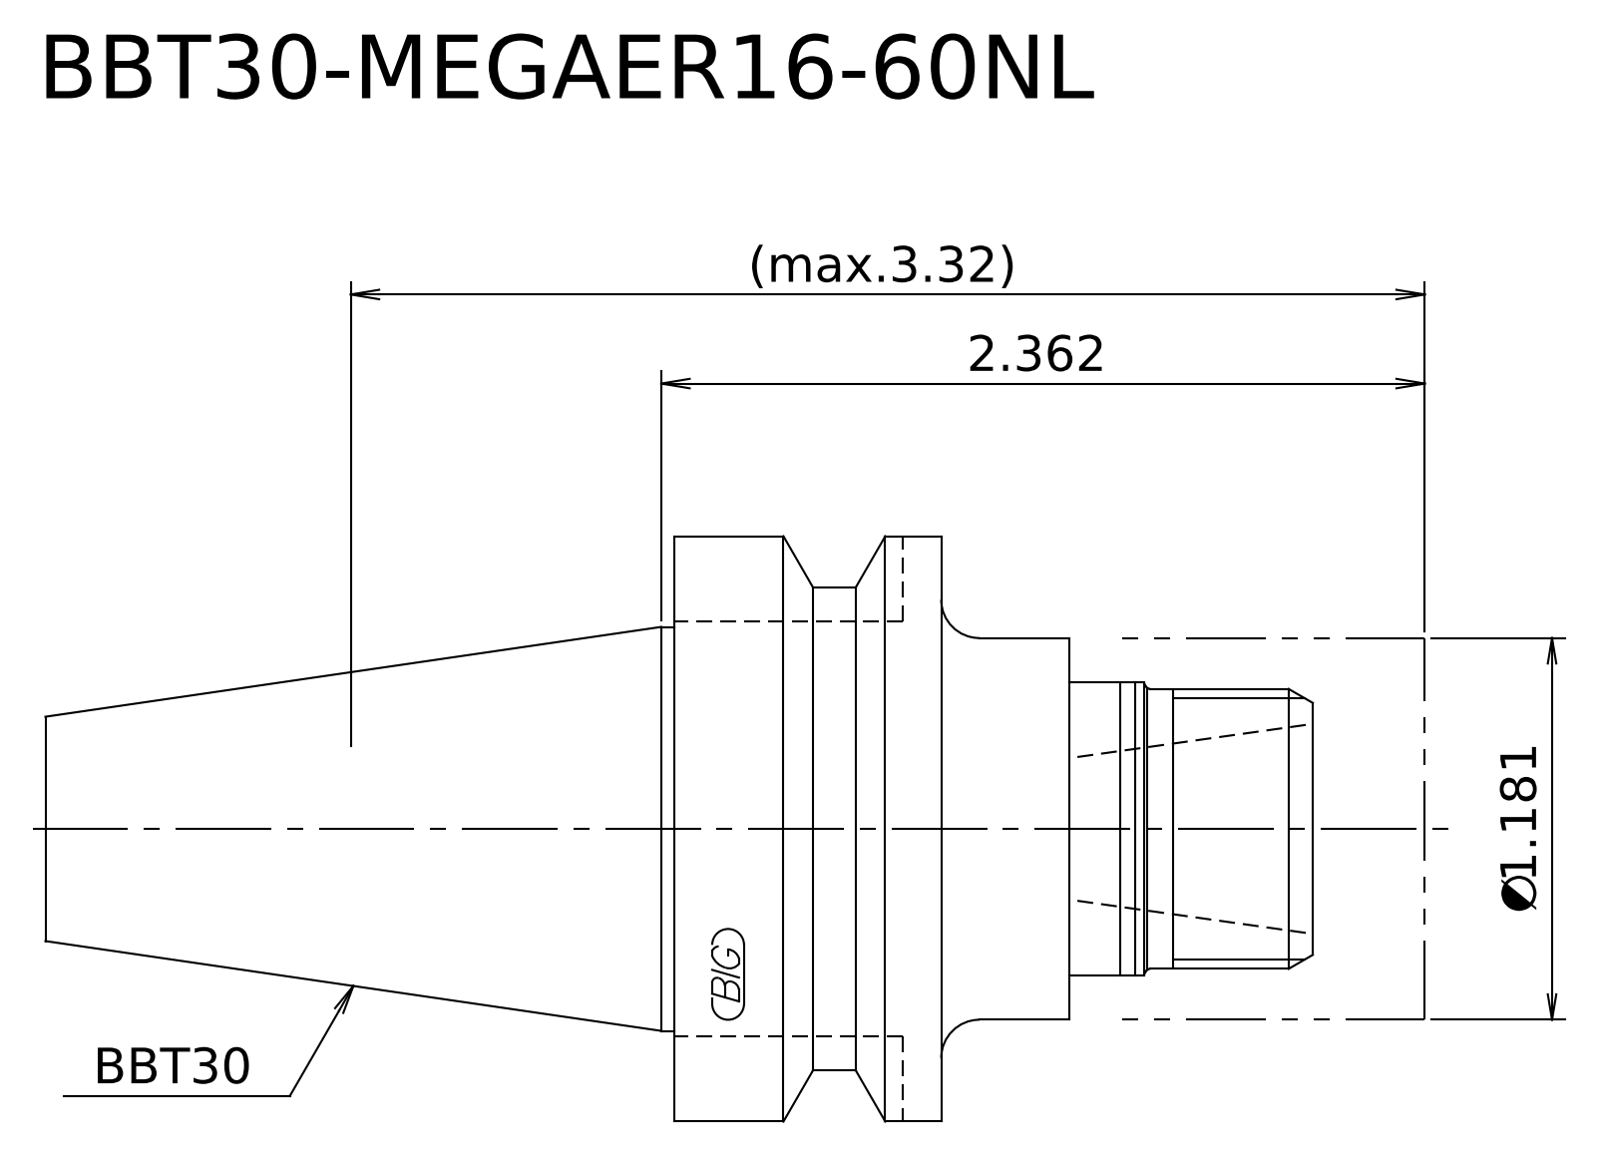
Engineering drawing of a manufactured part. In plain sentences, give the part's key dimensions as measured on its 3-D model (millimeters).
Its 3-D file was written by "Kubotek KeyCreator 2011 V10.0.2 (22737) (automotive_design)". It is 2 solids with 21 faces: 7 planar, 8 cylindrical and 6 other. Overall it measures 108.4 by 46 by 46 millimeters. Its volume is 89 121 cubic millimeters and its surface area 16 004 square millimeters. Round bosses or shafts: 1 of diameter 46, 1 of diameter 38, 1 of diameter 31.75, 1 of diameter 30, 1 of diameter 23, 1 of diameter 22. The main face-to-face distances are 34, 25, 59, 38, 13, 21, 8.8, 16.2, 29.2, 50.2.
